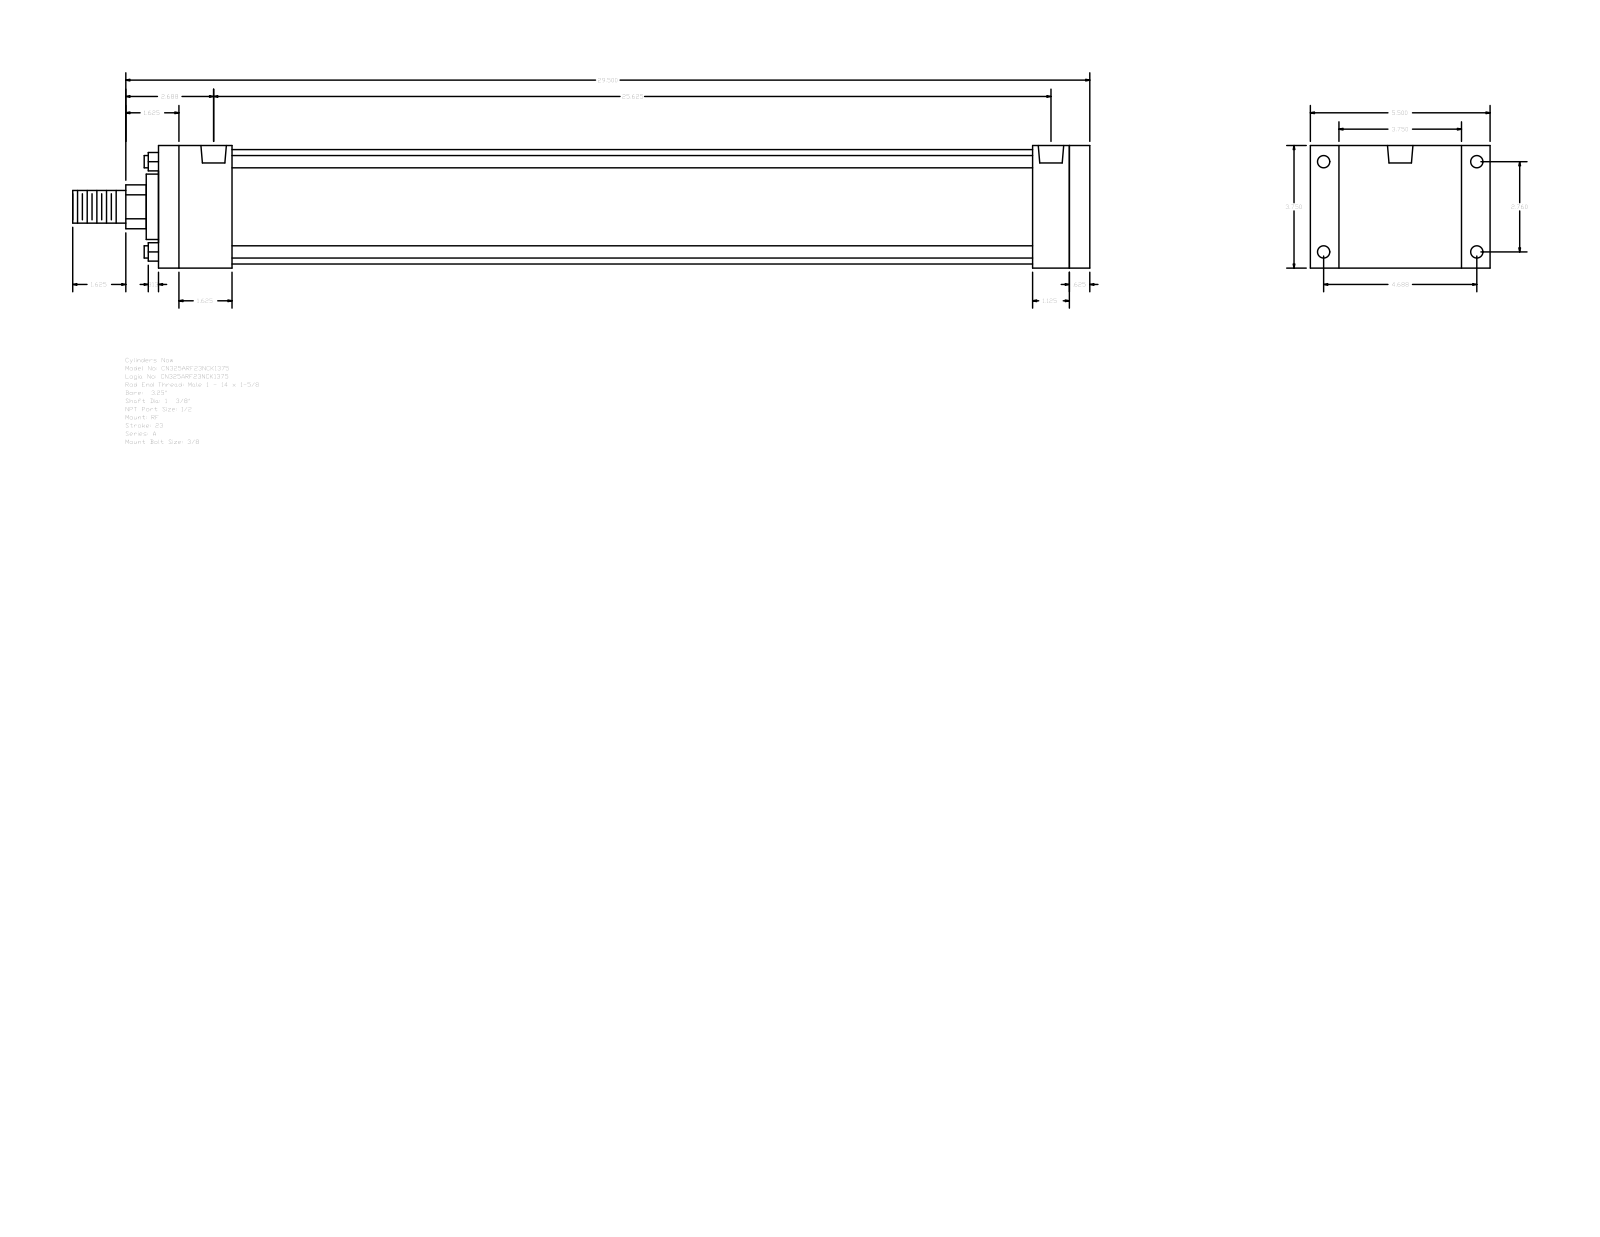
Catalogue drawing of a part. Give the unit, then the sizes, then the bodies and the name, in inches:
Units: inches
Overall size (bounding box): 31.125 × 5.5 × 3.75
Round holes (diameter × count): ⌀0.344 ×4, ⌀0.375 ×4, ⌀0.778 ×2
Round bosses / shafts (diameter × count): ⌀0.375 ×4, ⌀3.5 ×1, ⌀2 ×1, ⌀1.375 ×1, ⌀1 ×1
Partial cylindrical surfaces — rounded edges, fillets, slot ends (radius × count): R0.672 ×1
Main face-to-face distances: 3.75, 28.5, 0.625, 27.875, 2.25, 0.875, 4.625, 26.75, 1.125, 1.75
Hole centre spacings: 0.125, 2.76, 4.687, 5.439, 25.375, 25.5, 25.625
Bodies: 0 solids, 92 faces (64 planar, 28 cylindrical, 0 other)
Part name (STEP PRODUCT): A_RF__0325_1.375
STEP written by: GSSL Pune (CONFIG_CONTROL_DESIGN)
